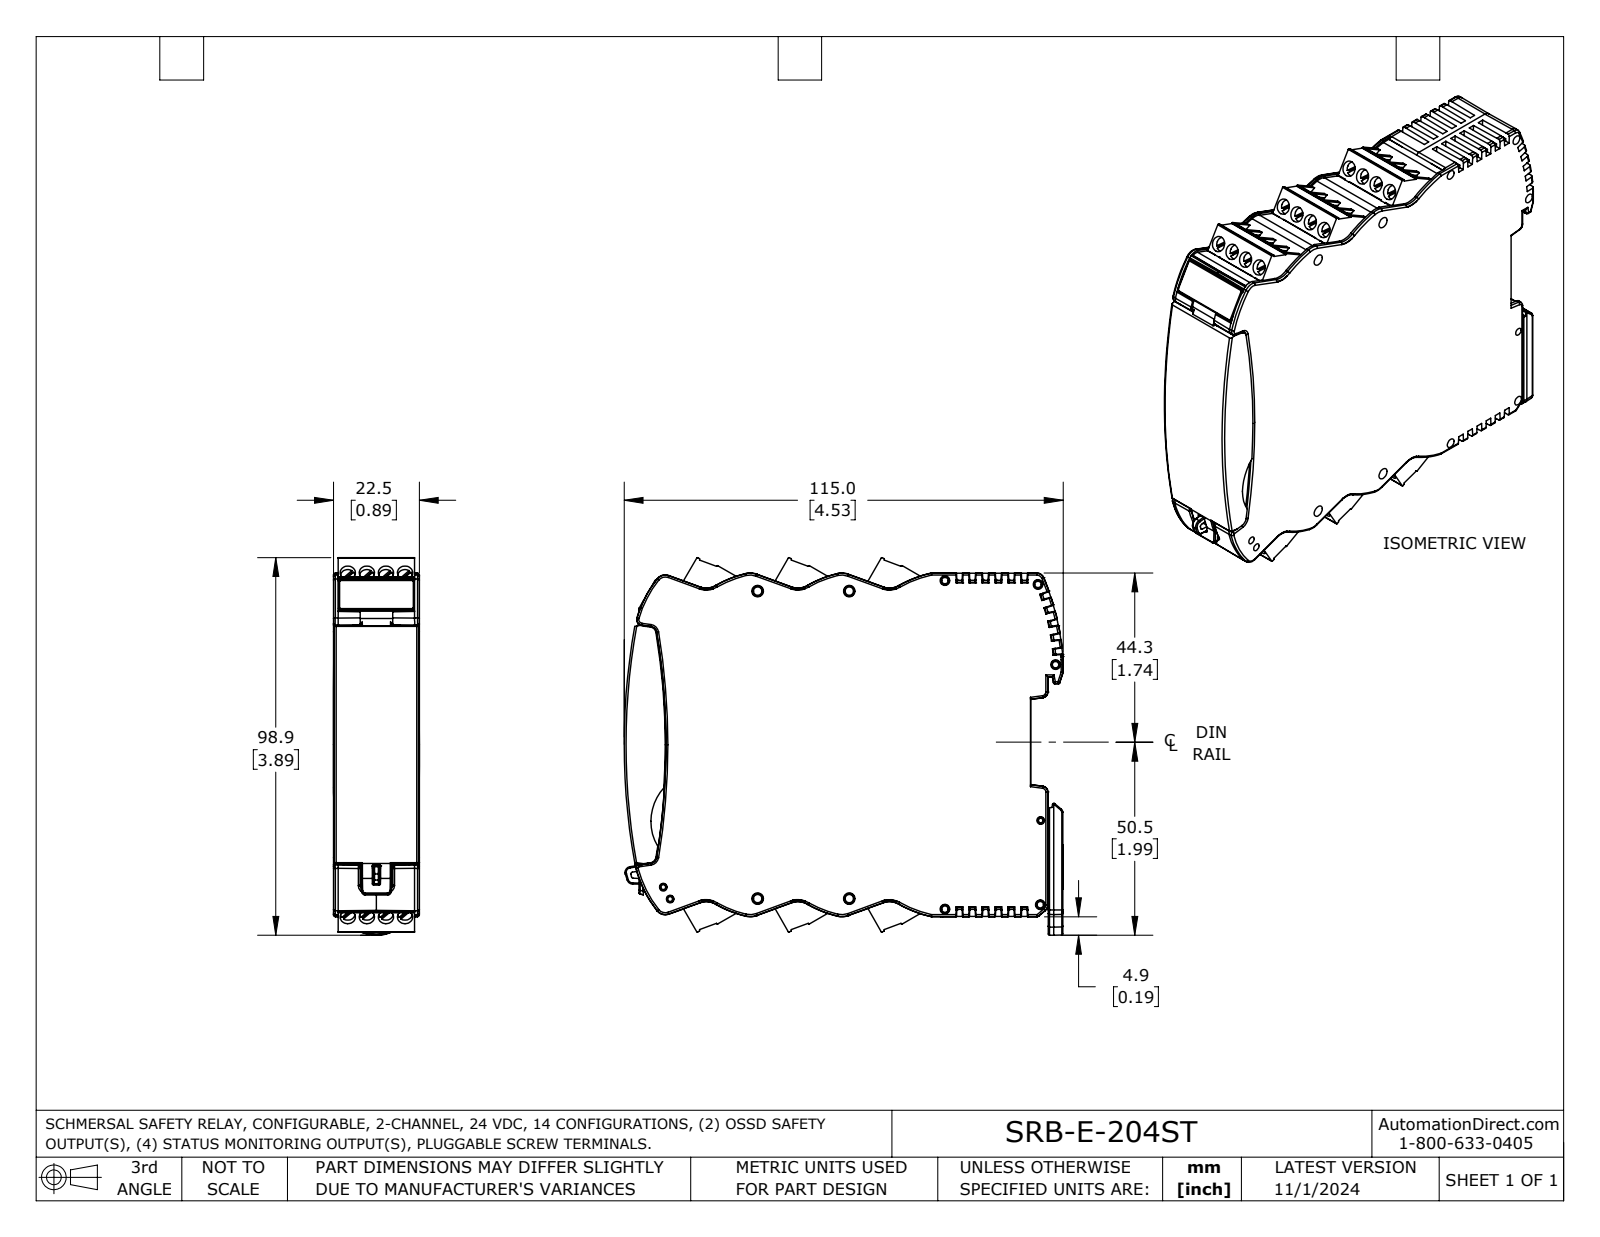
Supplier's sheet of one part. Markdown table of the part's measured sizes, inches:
| quantity | value |
| --- | --- |
| part name | SRB-E-204ST |
| STEP written by | SolidWorks 2023 (AUTOMOTIVE_DESIGN) |
| units | inches |
| bodies | 2 solids, 2923 faces (1586 planar, 682 cylindrical, 655 other) |
| overall size | 4.528 × 3.893 × 0.886 |
| volume | 13.02 in³ |
| surface area | 65.67 in² |
| round holes (diameter × count) | 0.157 × 24 |
| round bosses / shafts (diameter × count) | 0.149 × 24, 0.067 × 1 |
| partial cylindrical surfaces (radius × count) | 0.012 × 175, 0.02 × 117, 0.01 × 36, 0.008 × 35, 0.059 × 26, 0.039 × 20, 0.079 × 8, 0.071 × 6 |
| main face-to-face distances | 0.886, 0.049, 0.837, 0.133, 0.035, 0.267, 0.134, 0.014, 0.85, 0.801 |
| hole center spacings | 0.197, 0.394, 0.512, 0.518, 0.972, 0.472, 0.479, 0.615 |
